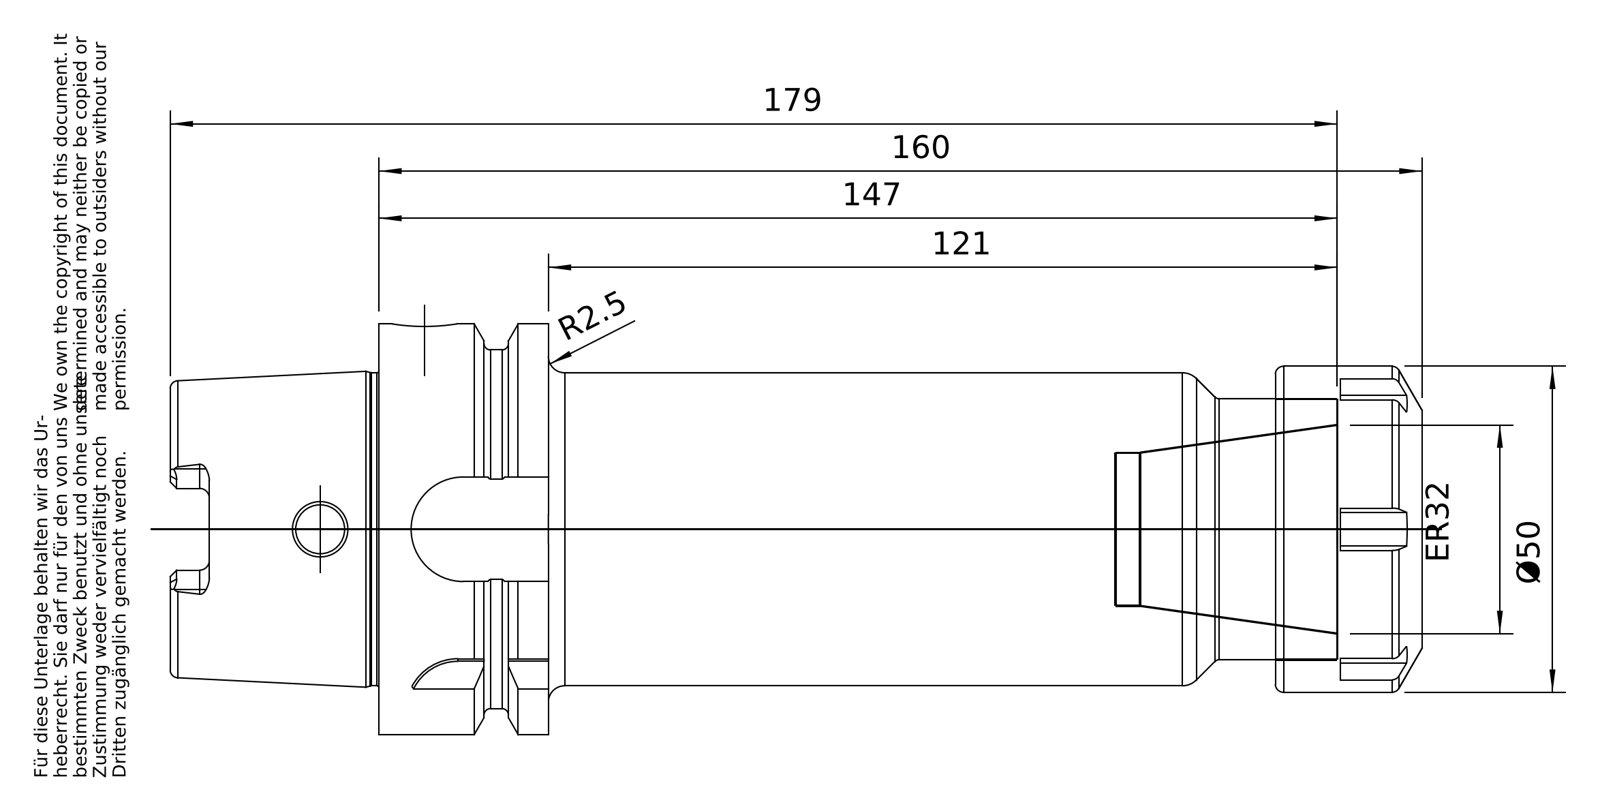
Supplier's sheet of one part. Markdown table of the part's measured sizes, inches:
| quantity | value |
| --- | --- |
| part name | A63-022-32; 83-912-32; A63-022-32_ASM |
| STEP written by | PRO/ENGINEER BY PARAMETRIC TECHNOLOGY CORPORATION, 2010430 (CONFIG_CONTROL_DESIGN) |
| units | inches |
| bodies | 2 solids, 224 faces (84 planar, 58 cylindrical, 82 other) |
| overall size | 7.559 × 2.48 × 2.48 |
| volume | 18.92 in³ |
| surface area | 76.78 in² |
| round holes (diameter × count) | 0.295 × 1, 0.394 × 1, 0.666 × 1, 0.721 × 1, 0.735 × 1, 0.925 × 1, 1.339 × 1, 1.575 × 1 |
| round bosses / shafts (diameter × count) | 2.48 × 1, 2.165 × 1, 1.969 × 1, 1.891 × 1, 1.89 × 1, 0.709 × 1 |
| partial cylindrical surfaces (radius × count) | 0.059 × 6, 0.106 × 6, 0.118 × 4, 0.315 × 1, 0.316 × 1, 0.355 × 1 |
| main face-to-face distances | 5.413, 6.299, 0.886, 1.024, 4.39, 5.276, 0.394, 0.63, 5.02, 5.906 |
